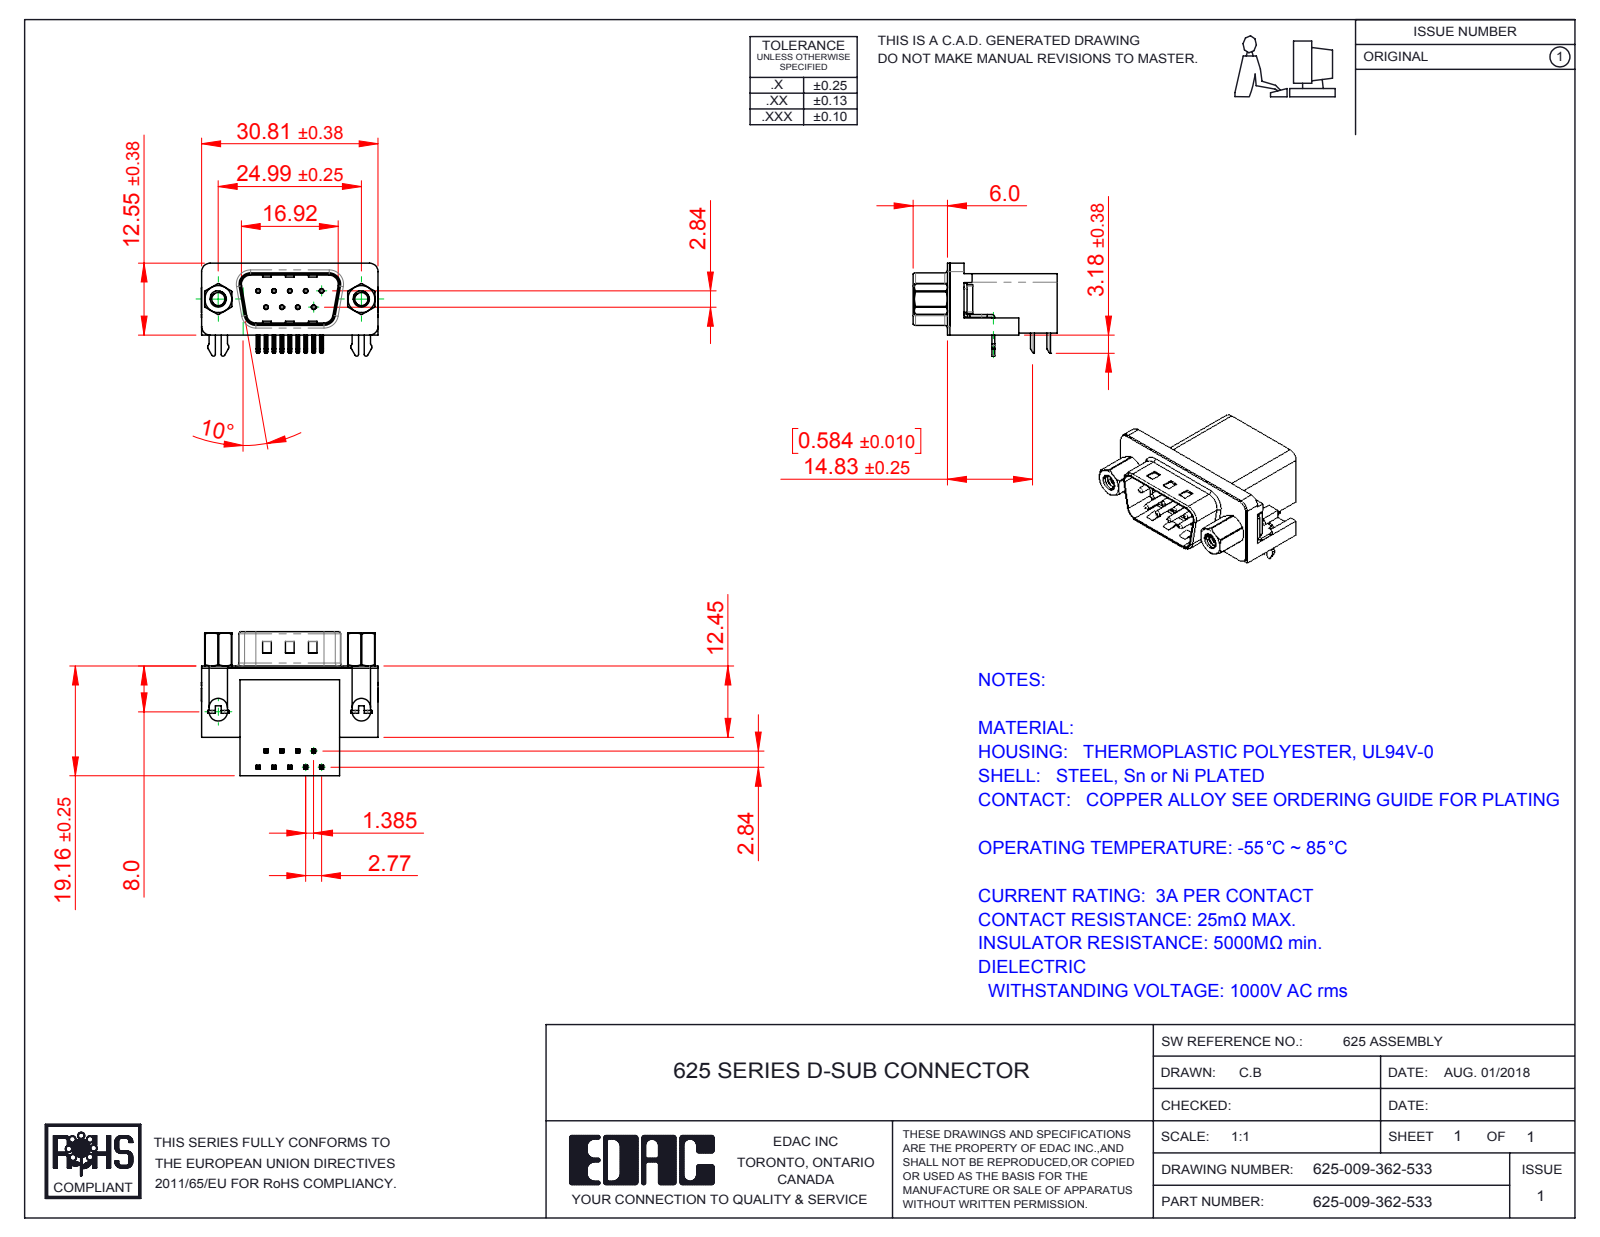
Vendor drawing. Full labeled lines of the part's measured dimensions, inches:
Part name (STEP PRODUCT): 625 Housing_9 Socket; 625-009-362-533; 625 2 Prong Board Lock; 625 4-40 Threaded Rivet (+4 more)
STEP written by: SolidWorks 2016 (CONFIG_CONTROL_DESIGN)
Units: inches
Bodies: 17 solids, 1159 faces (627 planar, 397 cylindrical, 135 other)
Overall size (bounding box): 1.216 × 0.991 × 0.64
Volume: 0.286 in³ · Surface area: 8.432 in²
Round holes (diameter × count): ⌀0.014 ×9, ⌀0.031 ×9, ⌀0.089 ×2, ⌀0.09 ×2, ⌀0.157 ×2, ⌀0.189 ×2, ⌀0.197 ×2
Round bosses / shafts (diameter × count): ⌀0.03 ×9, ⌀0.193 ×2, ⌀0.187 ×2, ⌀0.154 ×2, ⌀0.11 ×2
Partial cylindrical surfaces — rounded edges, fillets, slot ends (radius × count): R0.01 ×44, R0.005 ×18, R0.039 ×16, R0.02 ×14, R0.059 ×8, R0.063 ×8, R0.013 ×4, R0.035 ×4
Main face-to-face distances: 0.016, 0.407, 0.739, 0.754, 0.64, 0.098, 0.114, 0.014, 0.421, 0.02
Hole centre spacings: 0.124, 0.109, 0.218, 0.198, 0.198, 0.327, 0.294, 0.295
